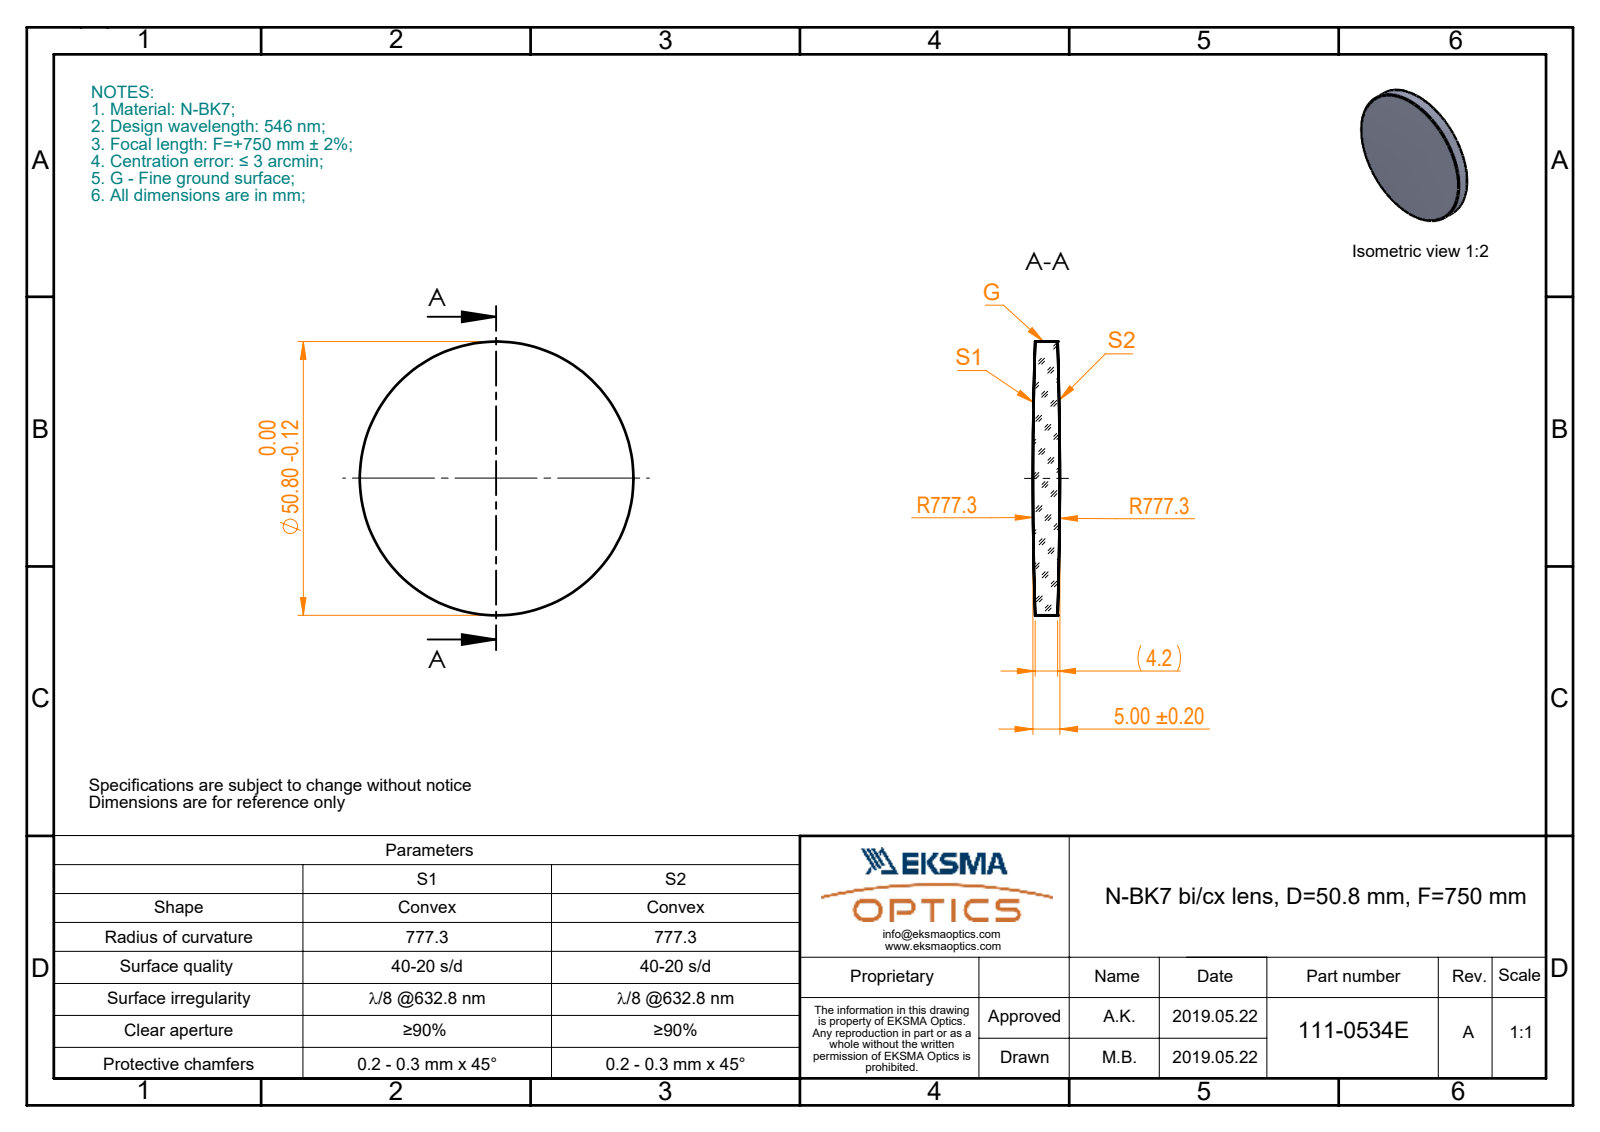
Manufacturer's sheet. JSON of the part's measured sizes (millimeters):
{"part_name": "111-0534E BK7 bi-cx 50.8 F750", "step_written_by": "SolidWorks 2017 (CONFIG_CONTROL_DESIGN)", "units": "millimeters", "bodies": {"solids": 1, "faces": 6, "planar": 0, "cylindrical": 2, "other": 4}, "overall_size": [50.8, 50.8, 5], "volume_mm3": 9293, "surface_area_mm2": 4720, "round_bosses_or_shafts": [[50.8, 1]]}
